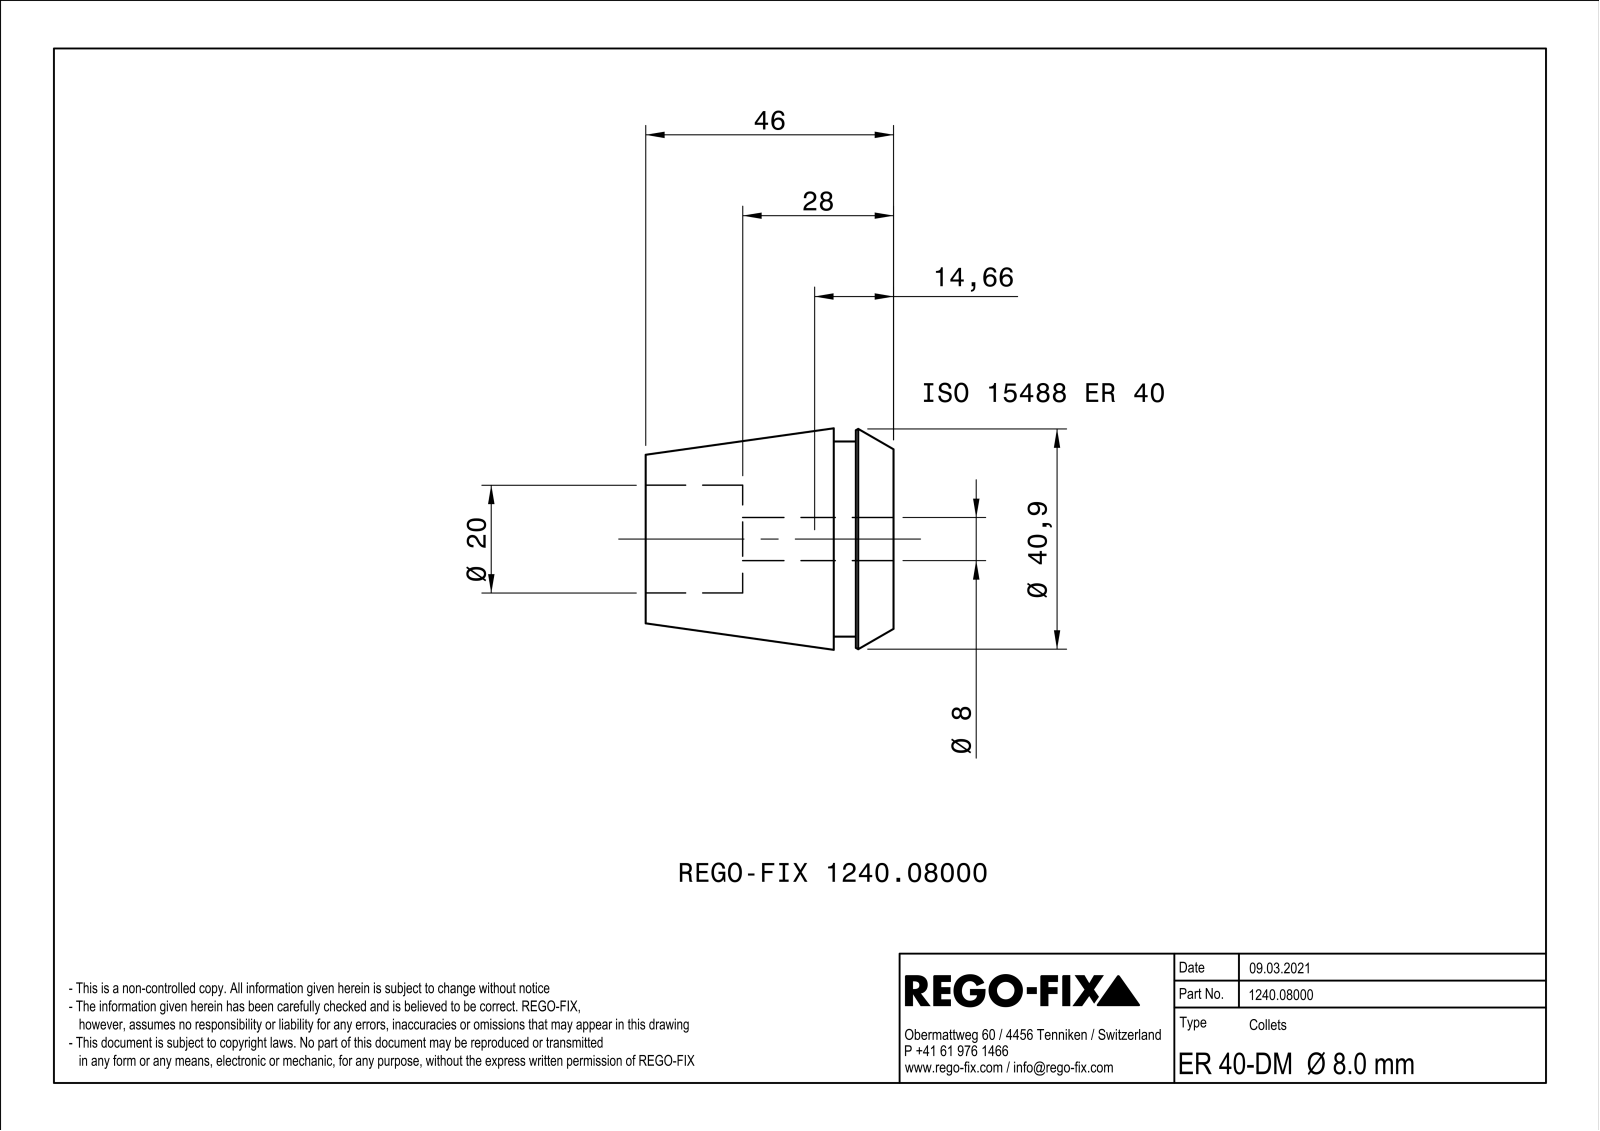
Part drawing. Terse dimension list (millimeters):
name: NOCUT
written by: SIEMENS PLM Software Solid Edge ST10 (AUTOMOTIVE_DESIGN)
unit: mm
bodies: 1 solid, 170 faces (88 planar, 17 cylindrical, 65 other)
size: 46 × 40.88 × 40.88
volume: 34 551 mm³; area: 19 110 mm²
holes: 1× ⌀8, 1× ⌀20
bosses: 1× ⌀36.2
face distances: 0.8, 46, 7, 39, 14, 11.1, 4.1, 34.9, 28, 21
